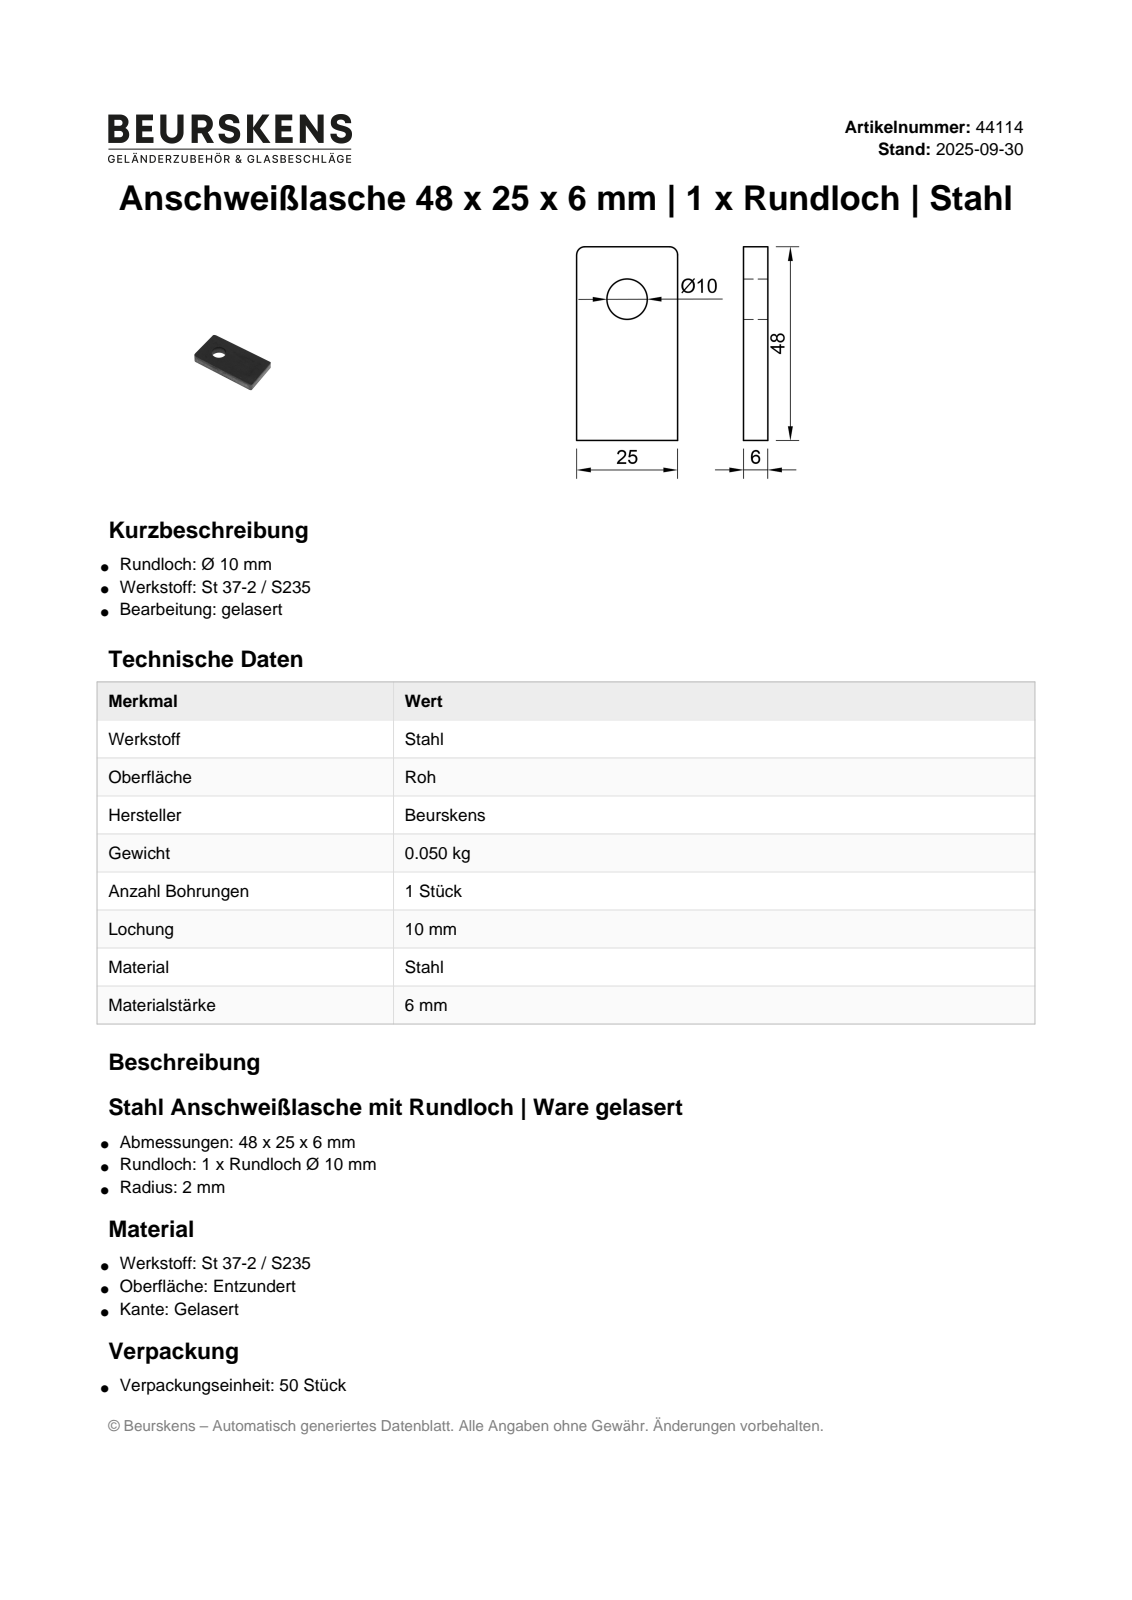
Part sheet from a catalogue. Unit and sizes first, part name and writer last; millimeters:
Units: millimetres
Overall size (bounding box): 48 × 25 × 6
Round holes (diameter × count): ⌀10 ×1
Partial cylindrical surfaces — rounded edges, fillets, slot ends (radius × count): R2 ×2
Main face-to-face distances: 6, 25, 48
Volume: 6 718 mm³ · Surface area: 3 294 mm²
Bodies: 1 solid, 9 faces (6 planar, 3 cylindrical, 0 other)
Part name (STEP PRODUCT): 44114
STEP written by: Autodesk Inventor 2023 (AUTOMOTIVE_DESIGN)
